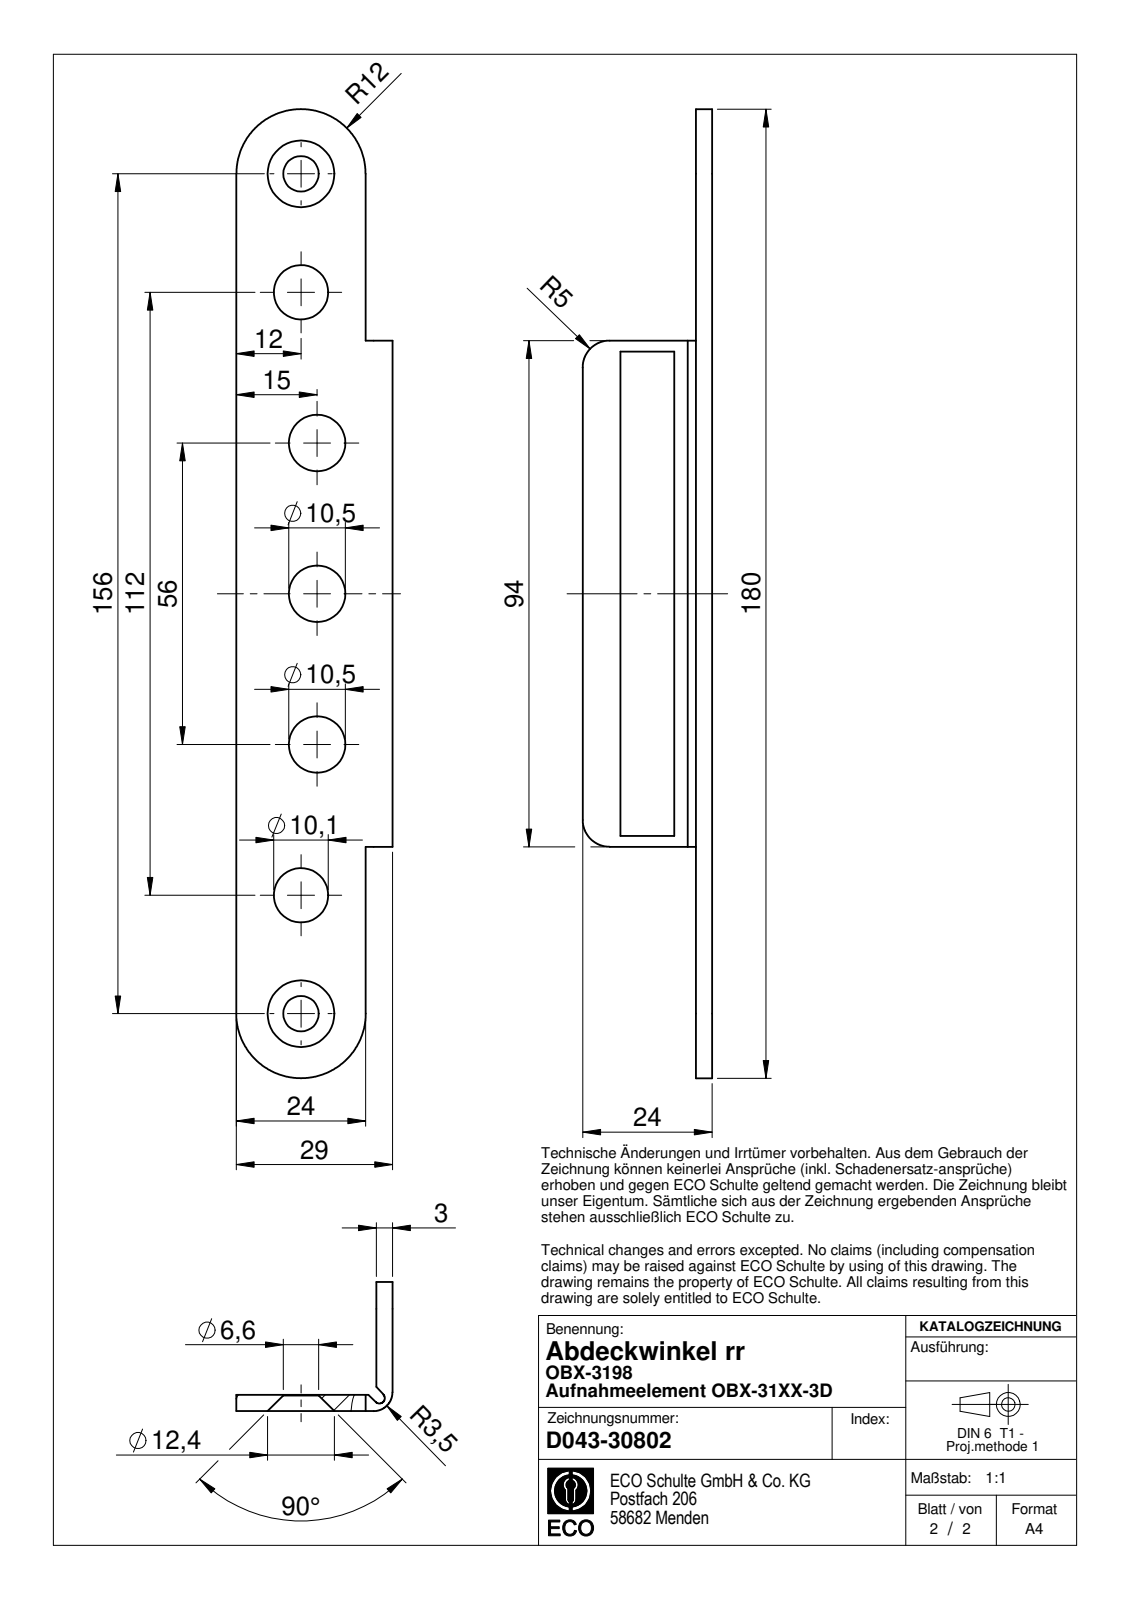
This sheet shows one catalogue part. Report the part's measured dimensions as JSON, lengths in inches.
{"part_name": "OBX-3198-rr_D043-30802", "step_written_by": "SolidWorks 2020 (AUTOMOTIVE_DESIGN)", "units": "inches", "bodies": {"solids": 1, "faces": 37, "planar": 14, "cylindrical": 19, "other": 4}, "overall_size": [7.087, 1.142, 0.945], "volume_in3": 0.931, "surface_area_in2": 19.85, "round_holes": [[0.413, 3], [0.26, 2], [0.398, 2]], "partial_cylinders_radius": [[0.197, 2], [0.472, 2], [0.138, 1]], "face_to_face_distances": [0.118, 0.276, 0.669, 1.024, 1.142, 0.945, 0.157, 0.394, 0.551, 0.827], "hole_center_spacings": [0.866, 1.102, 1.109, 1.972, 2.208, 3.073, 3.309, 4.175]}
